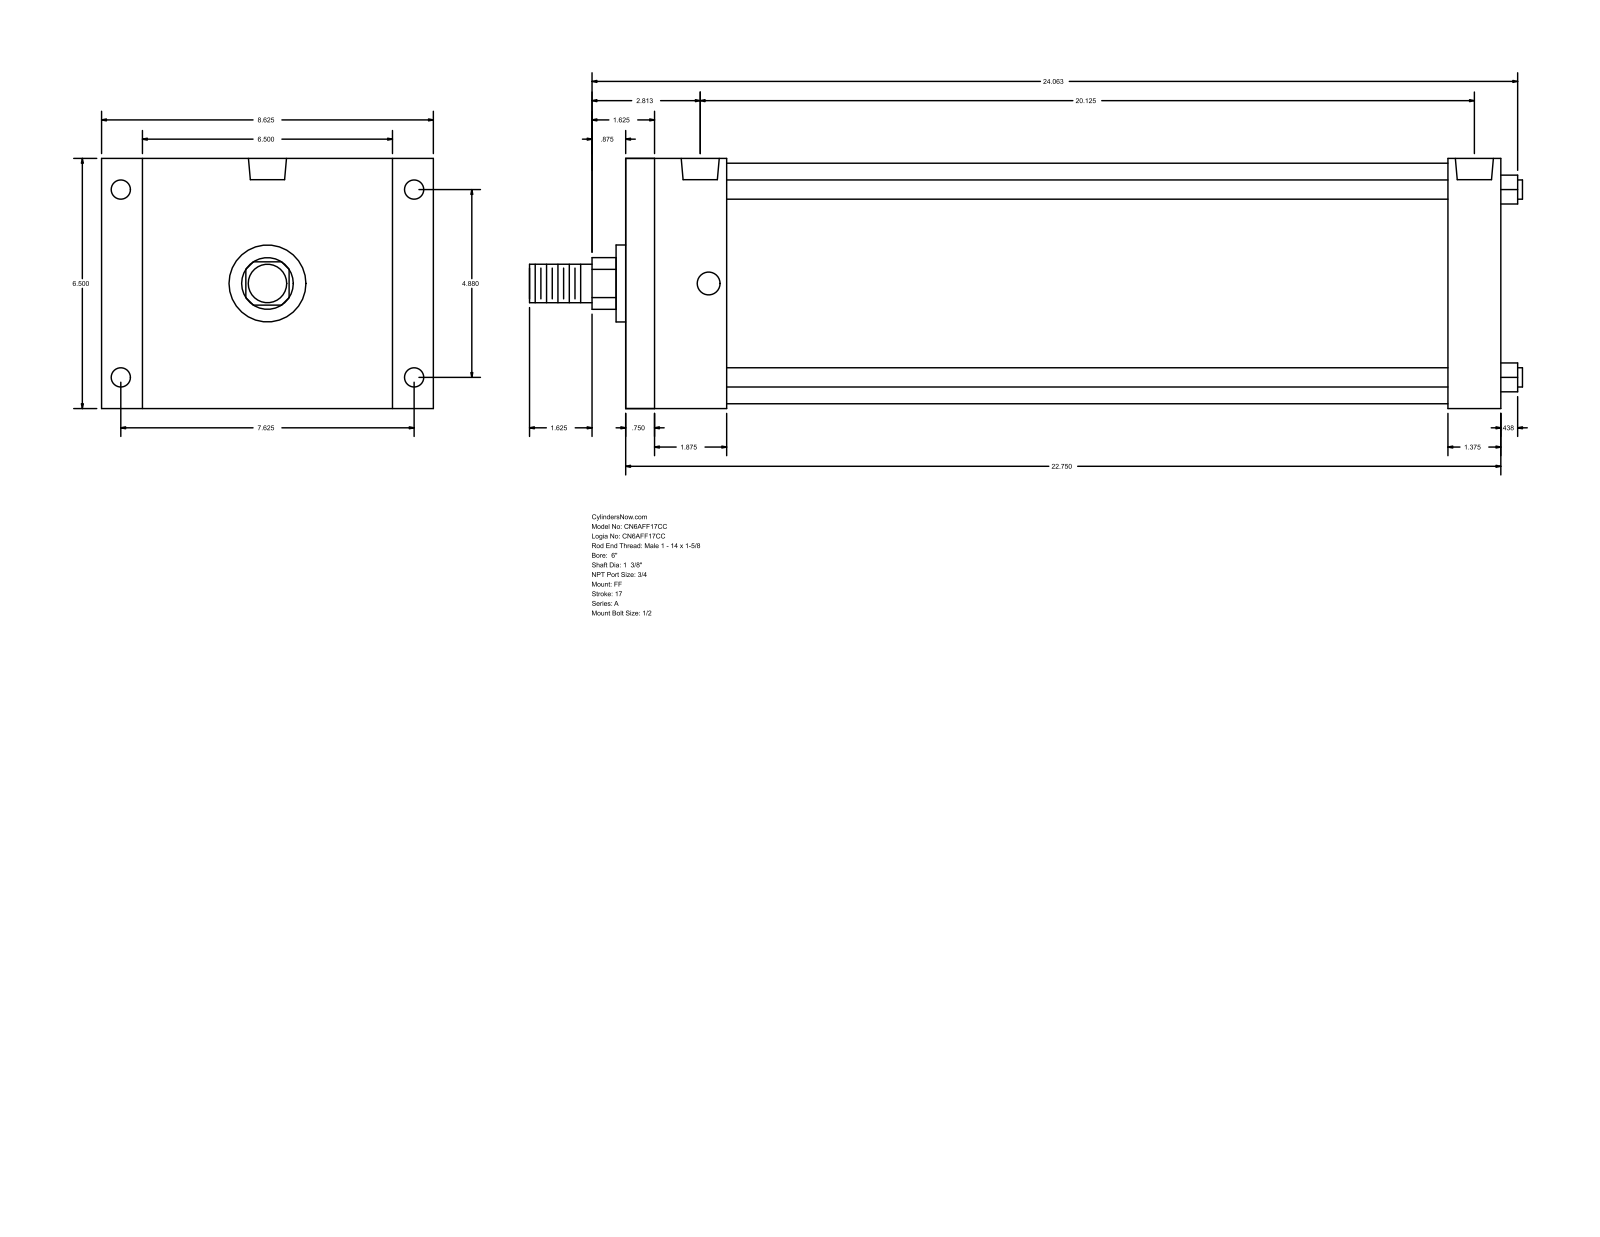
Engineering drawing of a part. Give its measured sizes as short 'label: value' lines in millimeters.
name: A_FF__0600_1.375
written by: GSSL Pune (CONFIG_CONTROL_DESIGN)
unit: mm
bodies: 0 solids, 92 faces (64 planar, 28 cylindrical, 0 other)
size: 655.64 × 219.07 × 165.1
holes: 4× ⌀12.7, 4× ⌀15.08, 2× ⌀25.12
bosses: 4× ⌀12.7, 1× ⌀158.75, 1× ⌀50.8, 1× ⌀34.92, 1× ⌀25.4
rounds: 1× R17.06
face distances: 165.1, 577.85, 19.04, 558.81, 66.67, 47.63, 511.18, 542.92, 523.88, 476.25
hole spacings: 5.56, 123.96, 193.68, 229.95, 500.05, 505.61, 511.17
